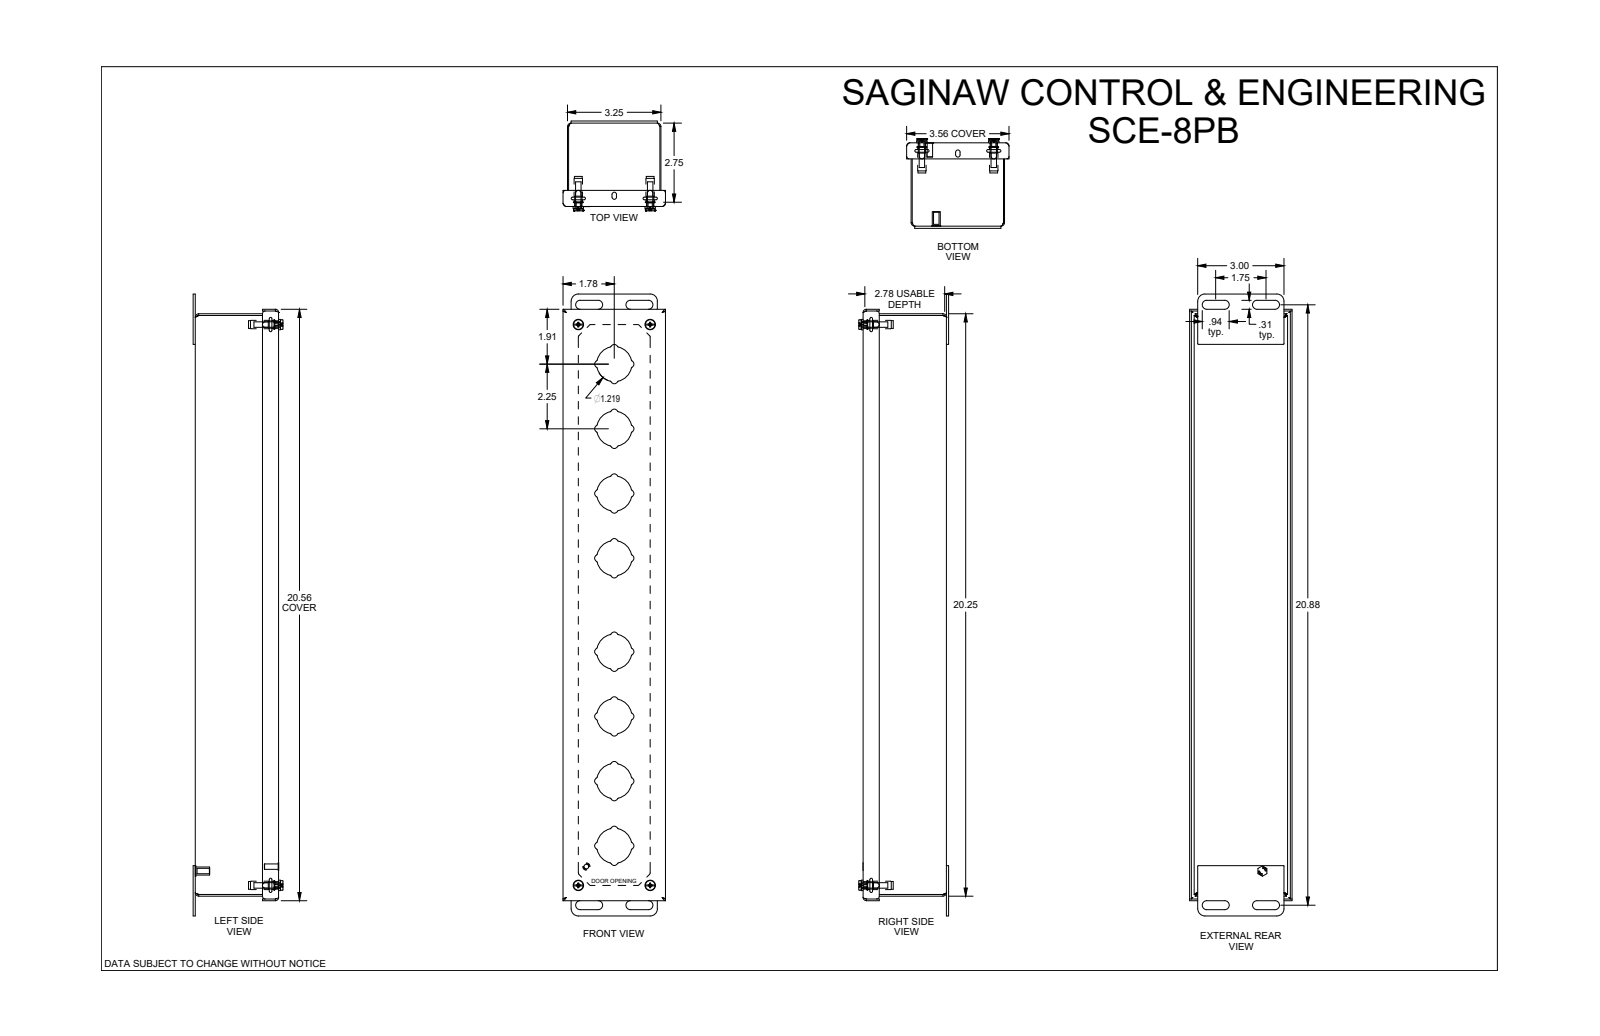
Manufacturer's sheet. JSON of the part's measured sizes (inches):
{"part_name": "SCE-8PB", "step_written_by": "SolidWorks 2021 (AUTOMOTIVE_DESIGN)", "units": "inches", "bodies": {"solids": 3, "faces": 544, "planar": 153, "cylindrical": 307, "other": 84}, "overall_size": [21.625, 3.563, 3.036], "volume_in3": 19.42, "surface_area_in2": 635.2, "round_holes": [[0.19, 5], [0.22, 4], [0.25, 4], [0.266, 4], [0.317, 4]], "round_bosses_or_shafts": [[0.362, 4], [0.34, 4], [0.292, 4], [0.27, 4], [0.26, 4], [0.28, 1], [0.256, 1], [0.188, 1]], "partial_cylinders_radius": [[0.04, 64], [0.125, 32], [0.06, 20], [0.015, 8], [0.115, 8], [0.156, 8], [0.245, 8], [0.609, 8]], "face_to_face_distances": [0.06, 2.838, 3.19, 2.778, 2.898, 3.25, 3.13, 0.156, 3.346, 2.69], "hole_center_spacings": [2.5, 19.5, 19.5, 19.659, 19.659, 2.5, 2.5, 0.7]}
